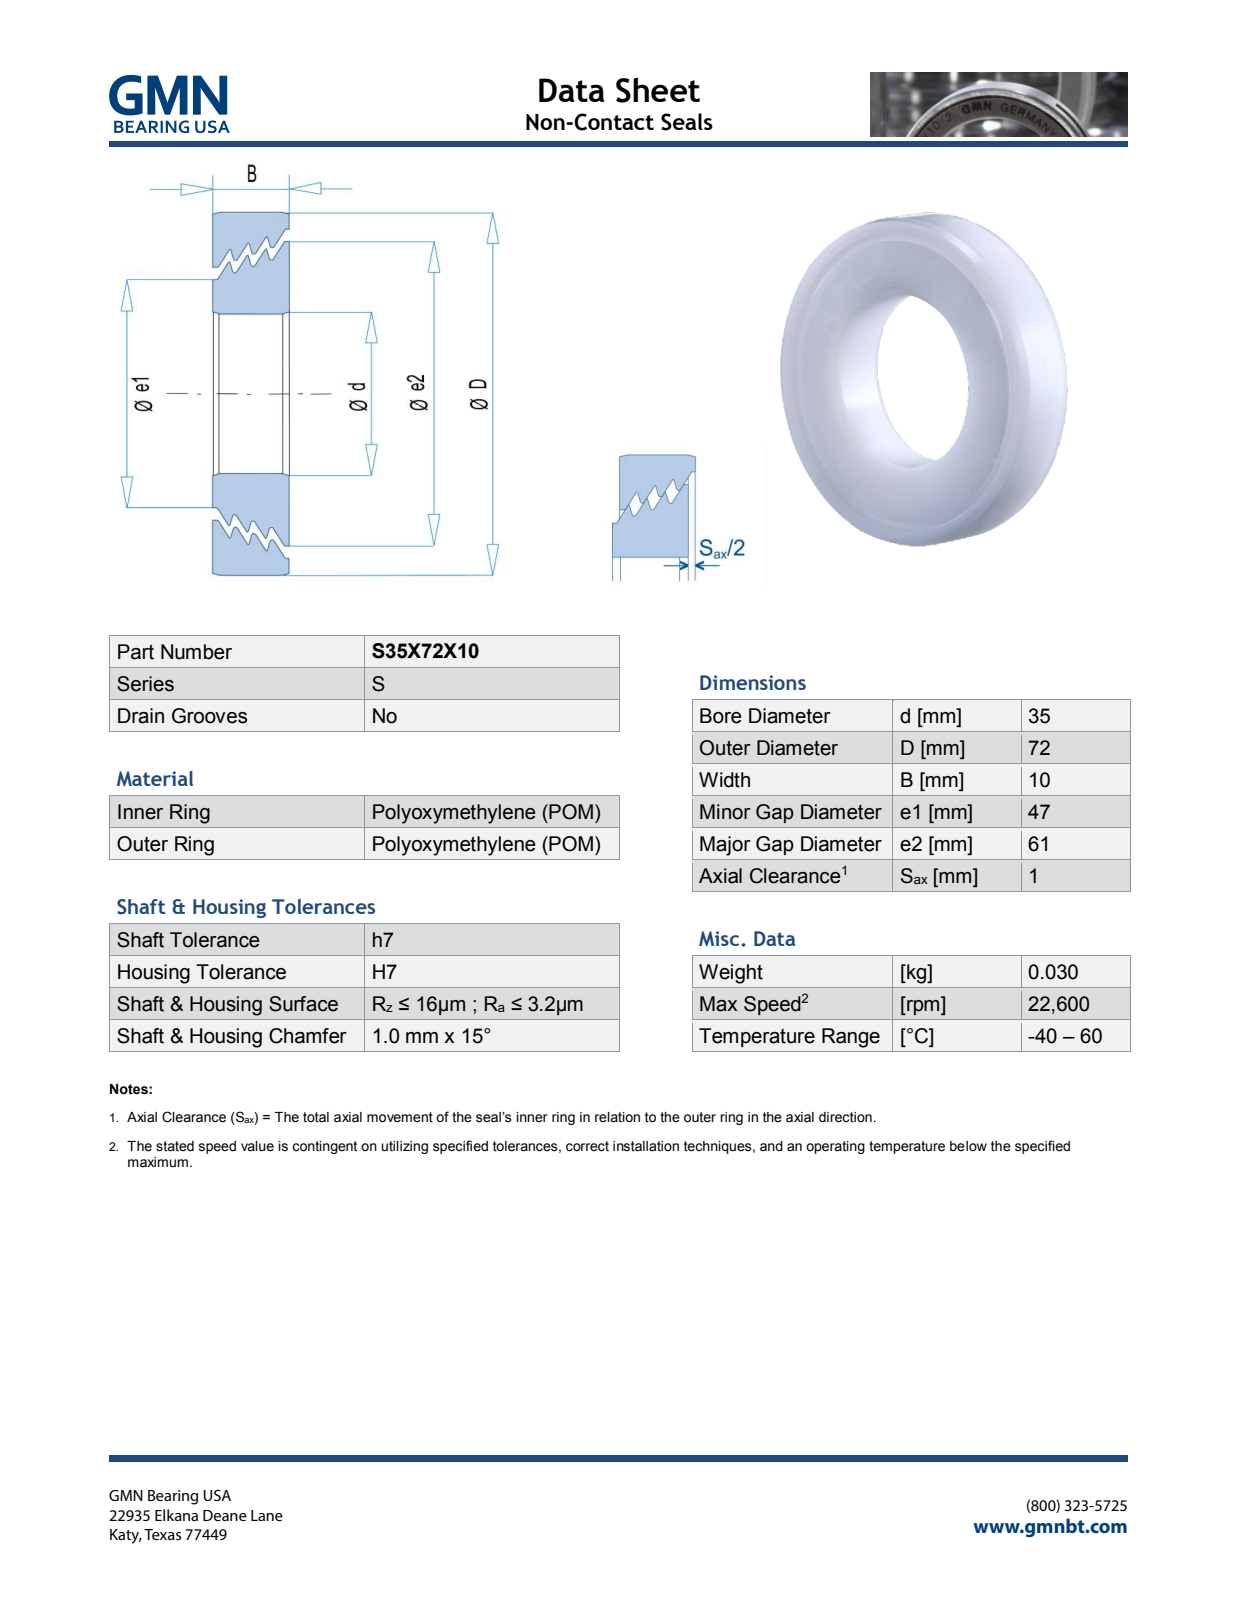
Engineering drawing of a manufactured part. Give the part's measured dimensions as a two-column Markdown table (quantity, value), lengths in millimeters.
| quantity | value |
| --- | --- |
| part name | S35X72X10_PRT |
| STEP written by | PRO/ENGINEER BY PARAMETRIC TECHNOLOGY CORPORATION, 2013150 (AUTOMOTIVE_DESIGN) |
| units | millimeters |
| bodies | 2 solids, 629 faces (549 planar, 12 cylindrical, 68 other) |
| overall size | 72 × 72 × 10.07 |
| volume | 29 605 mm³ |
| surface area | 16 047 mm² |
| round holes (diameter × count) | 35 × 1, 48.63 × 1, 62.63 × 1 |
| round bosses / shafts (diameter × count) | 72 × 1, 61 × 1, 47 × 1 |
| main face-to-face distances | 10, 10.07, 0.46, 0.45, 3.63, 3.18, 3.17, 0.41, 0.39, 0.38 |
